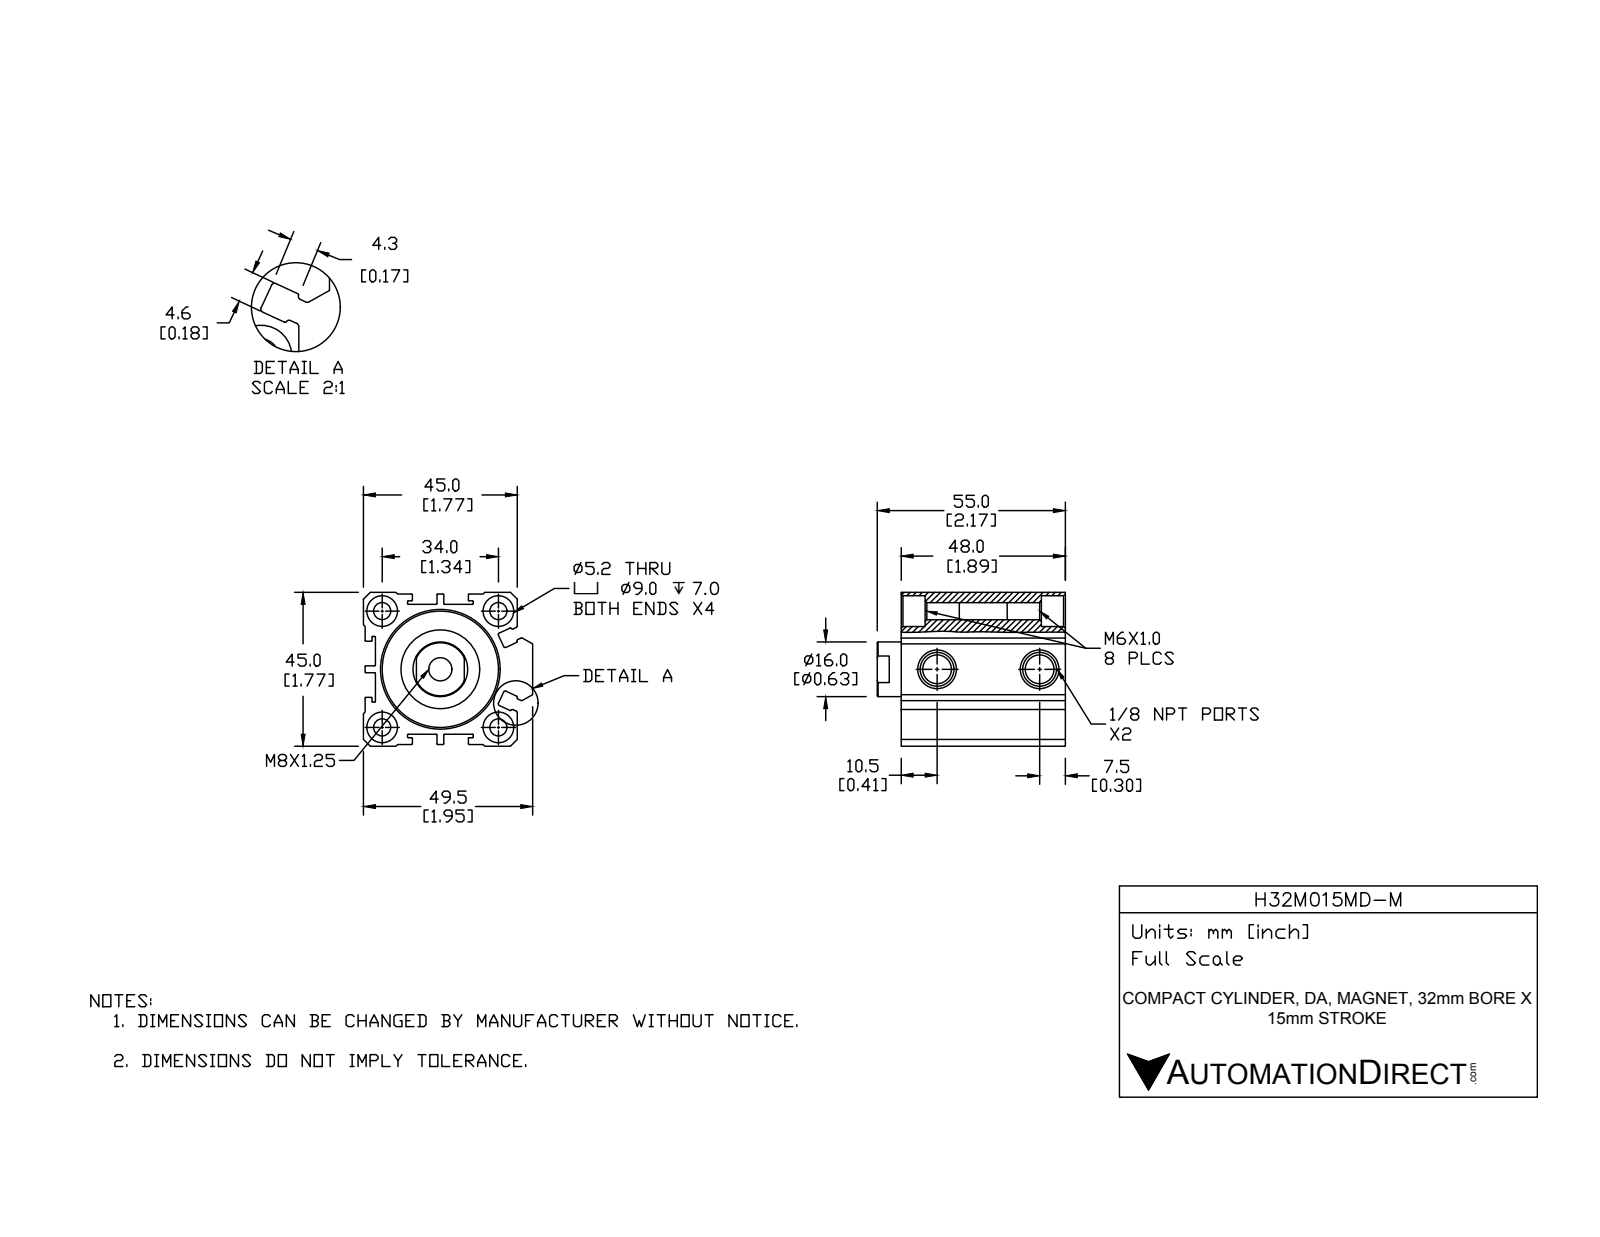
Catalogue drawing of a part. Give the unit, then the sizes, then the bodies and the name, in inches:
Units: inches
Overall size (bounding box): 2.165 × 1.949 × 1.772
Round holes (diameter × count): ⌀0.197 ×4, ⌀0.354 ×4, ⌀0.332 ×2, ⌀0.268 ×1, ⌀0.63 ×1, ⌀0.906 ×1, ⌀1.102 ×1, ⌀1.26 ×1, ⌀1.339 ×1
Round bosses / shafts (diameter × count): ⌀0.787 ×1
Partial cylindrical surfaces — rounded edges, fillets, slot ends (radius × count): R0.008 ×40, R0.02 ×12
Main face-to-face distances: 0.138, 1.634, 0.118, 1.772, 1.752, 0.177, 0.02, 1.614, 1.496, 0.827
Hole centre spacings: 0.946, 1.339, 1.893, 1.181
Volume: 4.32 in³ · Surface area: 48.16 in²
Bodies: 2 solids, 255 faces (99 planar, 103 cylindrical, 53 other)
Part name (STEP PRODUCT): H32M015MD-M-PISTON; H32M015MD-M; H32M015MD-M-BODY
STEP written by: SolidWorks 2015 (CONFIG_CONTROL_DESIGN)
